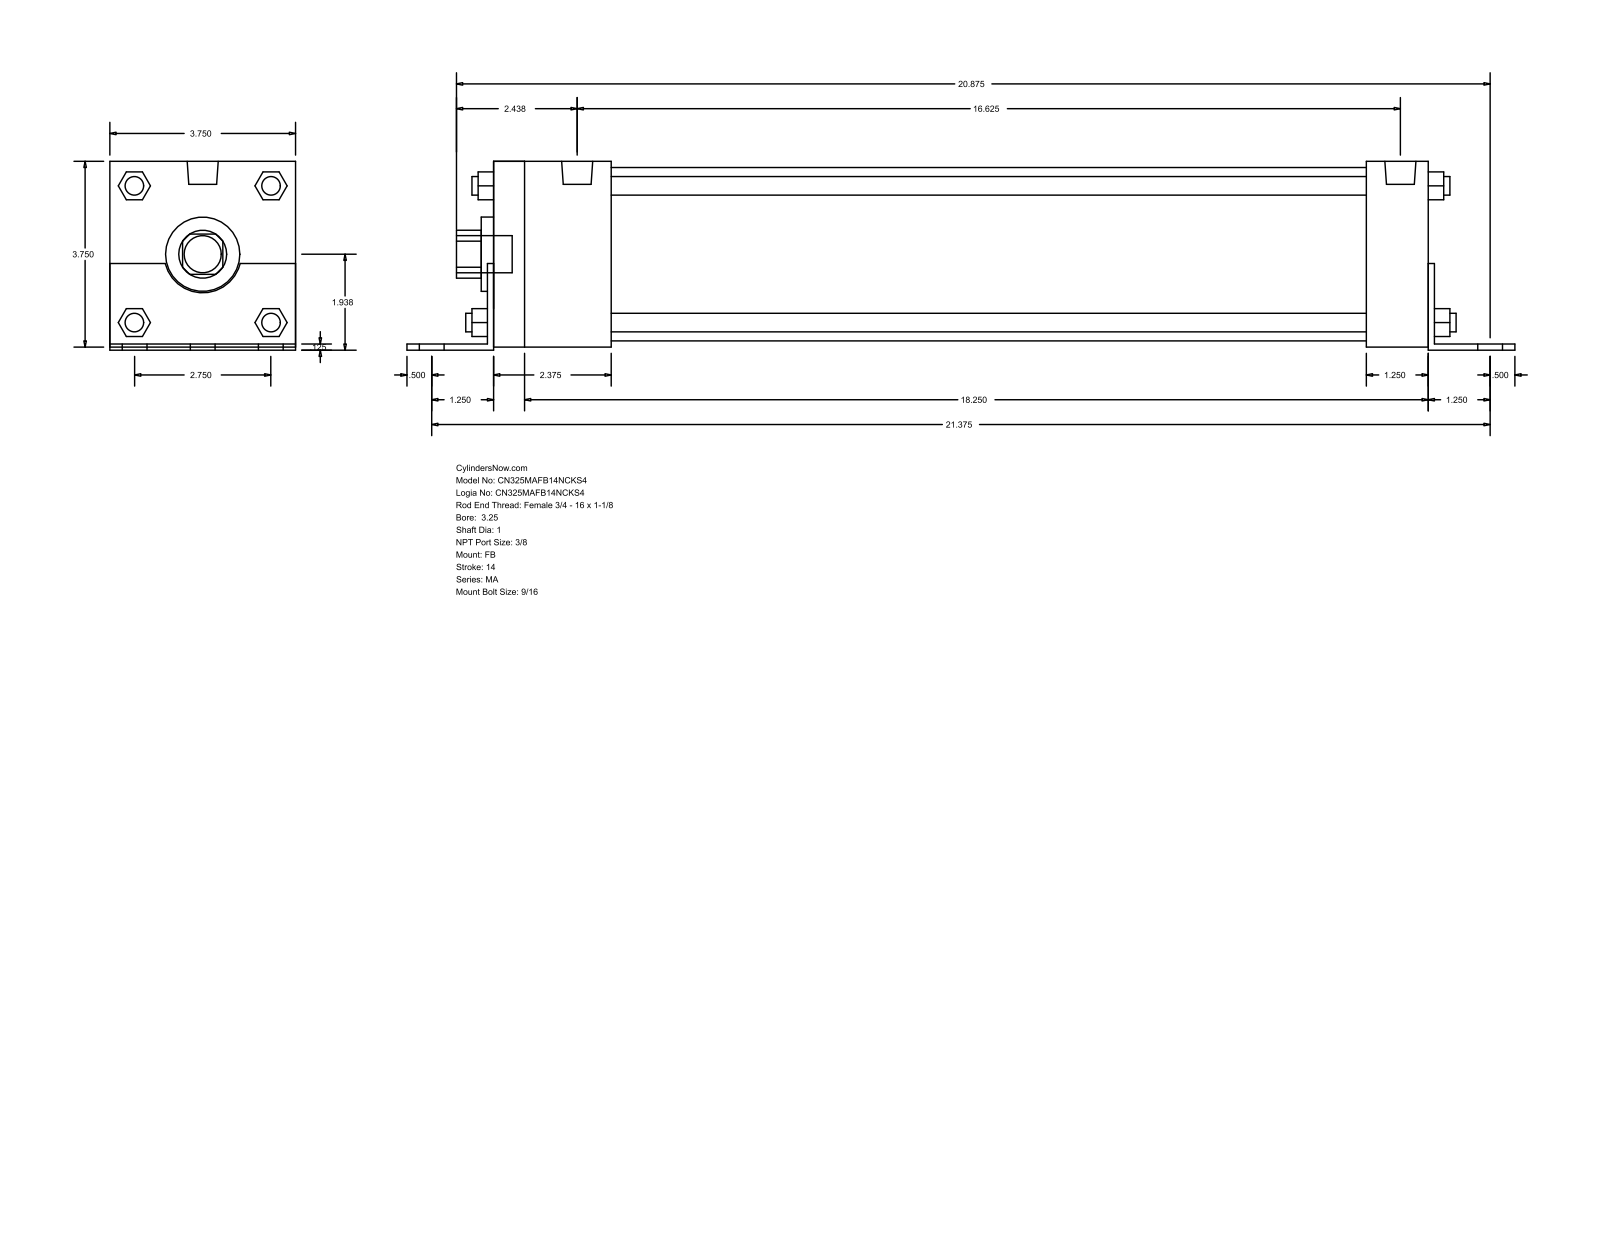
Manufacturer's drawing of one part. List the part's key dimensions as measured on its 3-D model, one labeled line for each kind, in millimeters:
Part name (STEP PRODUCT): MA_FB__0325_1
STEP written by: GSSL Pune (CONFIG_CONTROL_DESIGN)
Units: millimetres
Bodies: 0 solids, 140 faces (105 planar, 35 cylindrical, 0 other)
Overall size (bounding box): 568.33 × 96.84 × 95.25
Round holes (diameter × count): ⌀25.4 ×1, ⌀38.1 ×1, ⌀88.9 ×1
Round bosses / shafts (diameter × count): ⌀14.29 ×6, ⌀11.11 ×4, ⌀9.53 ×4, ⌀15.93 ×2, ⌀19.05 ×1
Partial cylindrical surfaces — rounded edges, fillets, slot ends (radius × count): R12.29 ×1, R19.81 ×1
Main face-to-face distances: 95.24, 3.17, 1.59, 96.83, 1.58, 93.66, 482.6, 479.43, 485.77, 450.85
